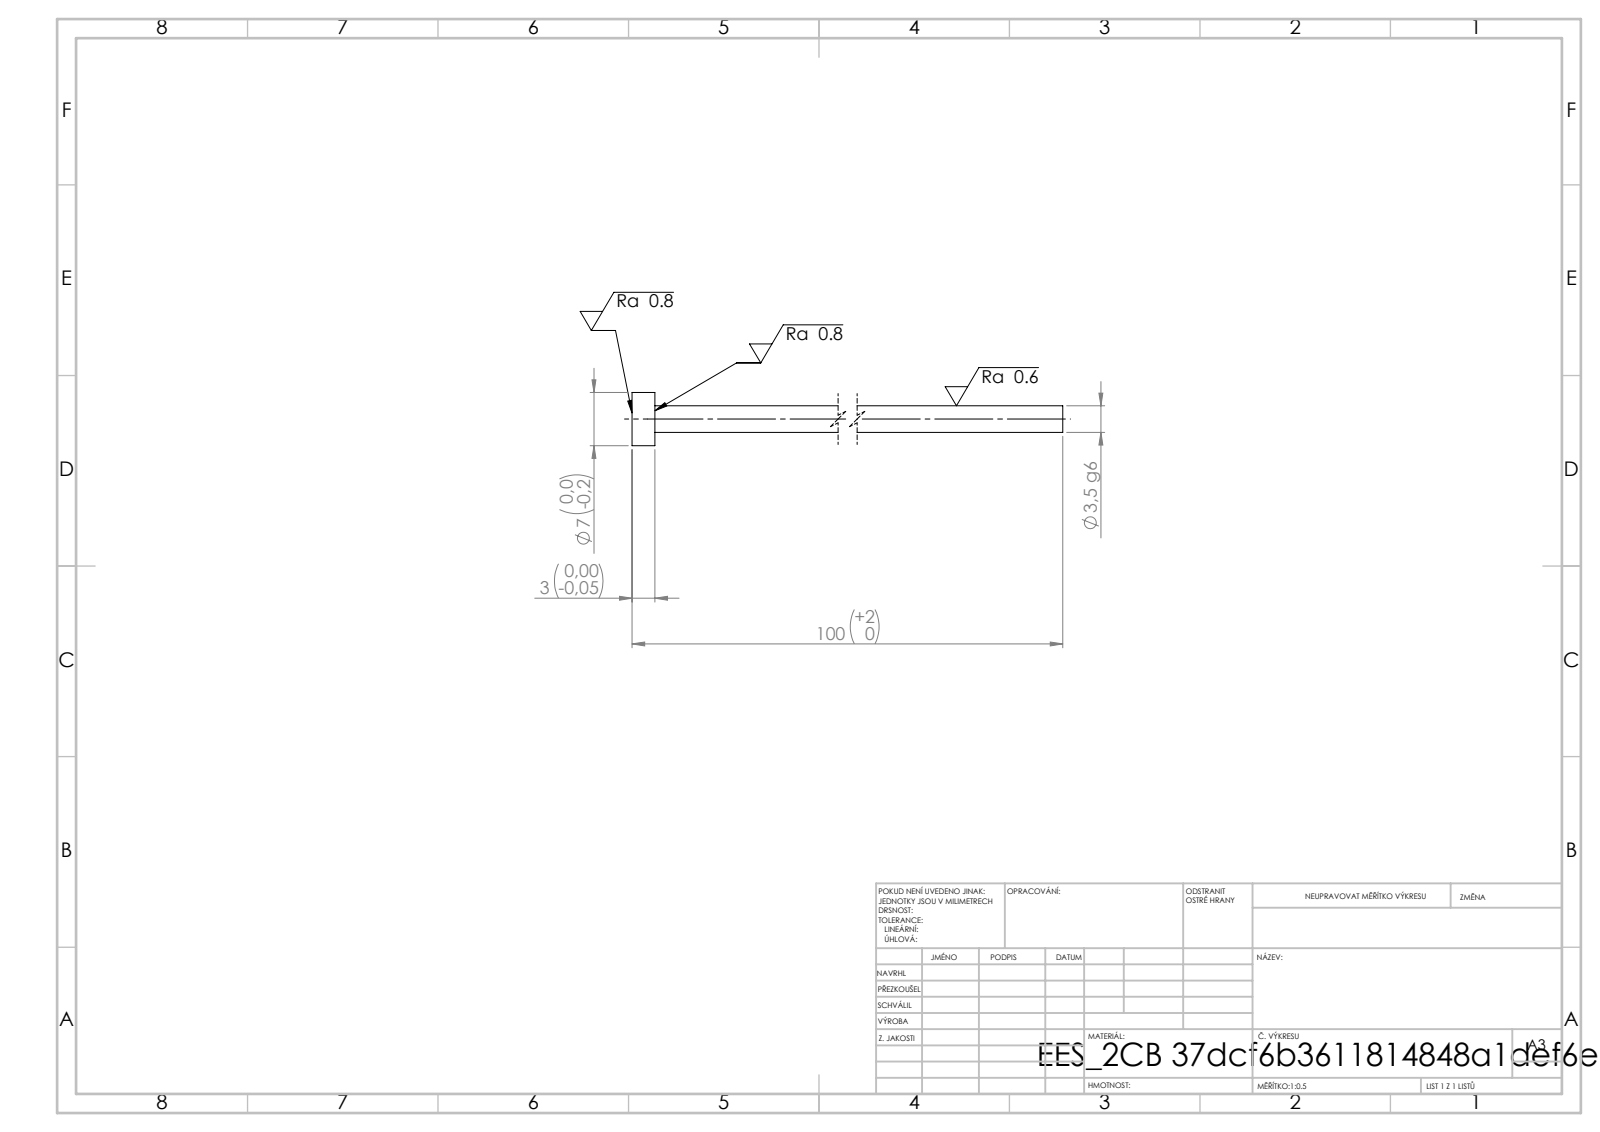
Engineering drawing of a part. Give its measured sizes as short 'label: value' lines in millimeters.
written by: SolidWorks 2019 (CONFIG_CONTROL_DESIGN)
unit: mm
bodies: 1 solid, 7 faces (3 planar, 4 cylindrical, 0 other)
size: 100 × 7 × 7
volume: 1 049 mm³; area: 1 210 mm²
bosses: 1× ⌀7, 1× ⌀3.5
face distances: 3, 100, 97
